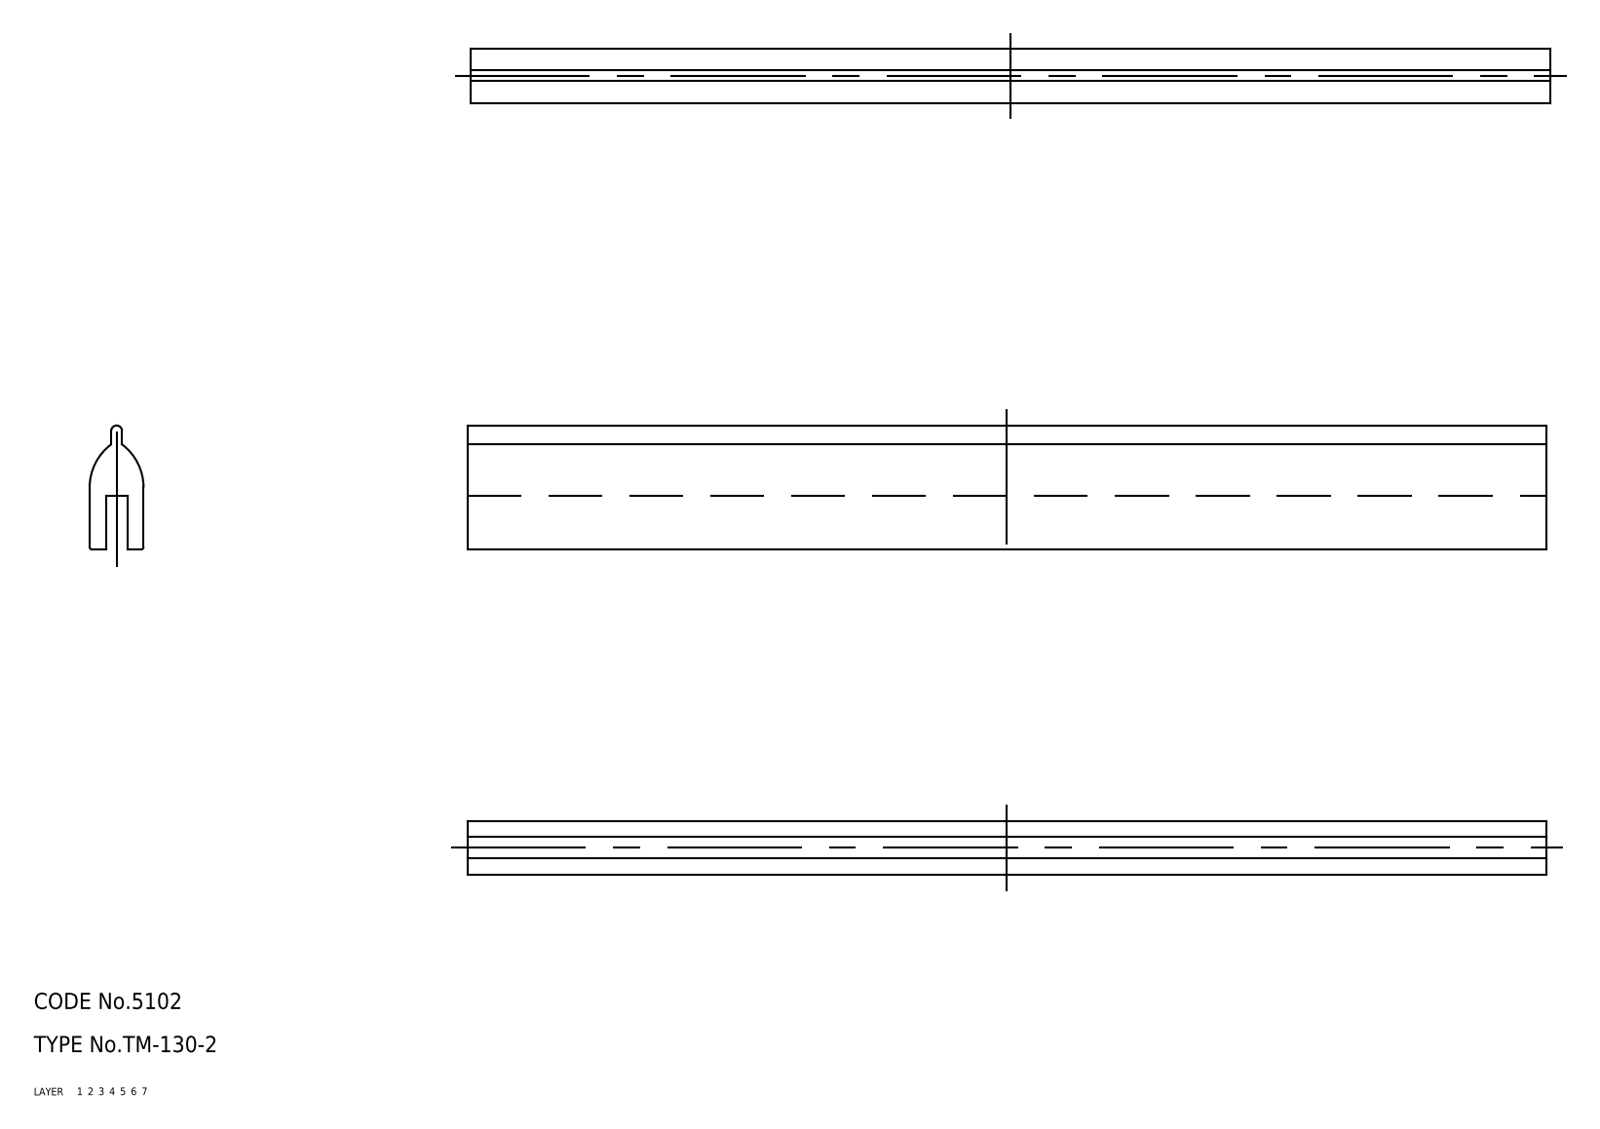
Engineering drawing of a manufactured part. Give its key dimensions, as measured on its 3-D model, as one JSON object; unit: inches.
{"part_name": "rubber foam", "step_written_by": "CADfix (AUTOMOTIVE_DESIGN)", "units": "inches", "bodies": {"solids": 1, "faces": 16, "planar": 0, "cylindrical": 0, "other": 16}, "overall_size": [7.874, 0.906, 0.394], "volume_in3": 1.735, "surface_area_in2": 25.01}
